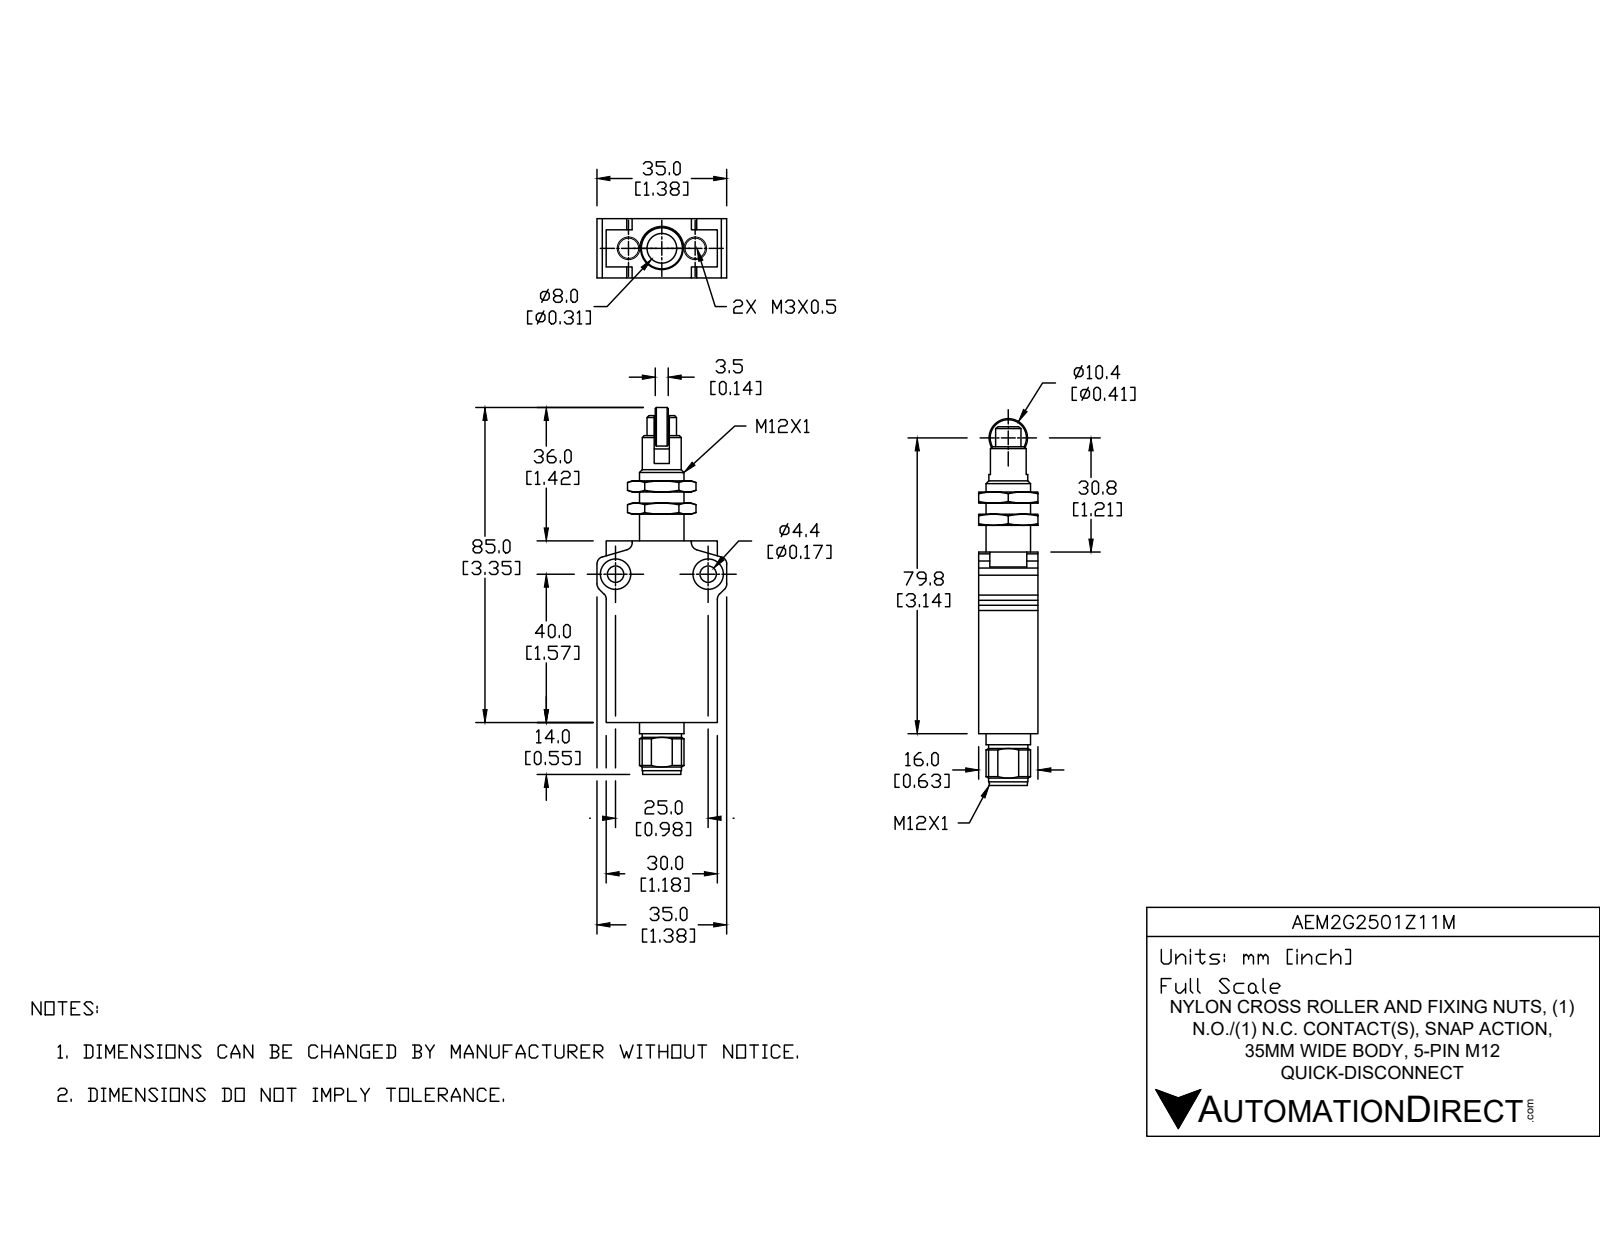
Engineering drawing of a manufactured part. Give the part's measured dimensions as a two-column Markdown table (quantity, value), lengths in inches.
| quantity | value |
| --- | --- |
| part name | AEM2G2501Z11M |
| STEP written by | SolidWorks 2017 (AUTOMOTIVE_DESIGN) |
| units | inches |
| bodies | 6 solids, 229 faces (82 planar, 76 cylindrical, 71 other) |
| overall size | 4.016 × 1.378 × 0.727 |
| volume | 1.785 in³ |
| surface area | 18.07 in² |
| round holes (diameter × count) | 0.118 × 2, 0.173 × 2, 0.323 × 2, 0.317 × 1 |
| round bosses / shafts (diameter × count) | 0.472 × 1, 0.417 × 1, 0.413 × 1, 0.409 × 1, 0.406 × 1, 0.313 × 1, 0.22 × 1 |
| partial cylindrical surfaces (radius × count) | 0.079 × 8, 0.256 × 1 |
| main face-to-face distances | 0.63, 1.181, 0.472, 0.118, 0.236, 2.047, 1.858, 0.189, 0.354, 0.157 |
| hole center spacings | 0.374, 0.748, 0.984 |
